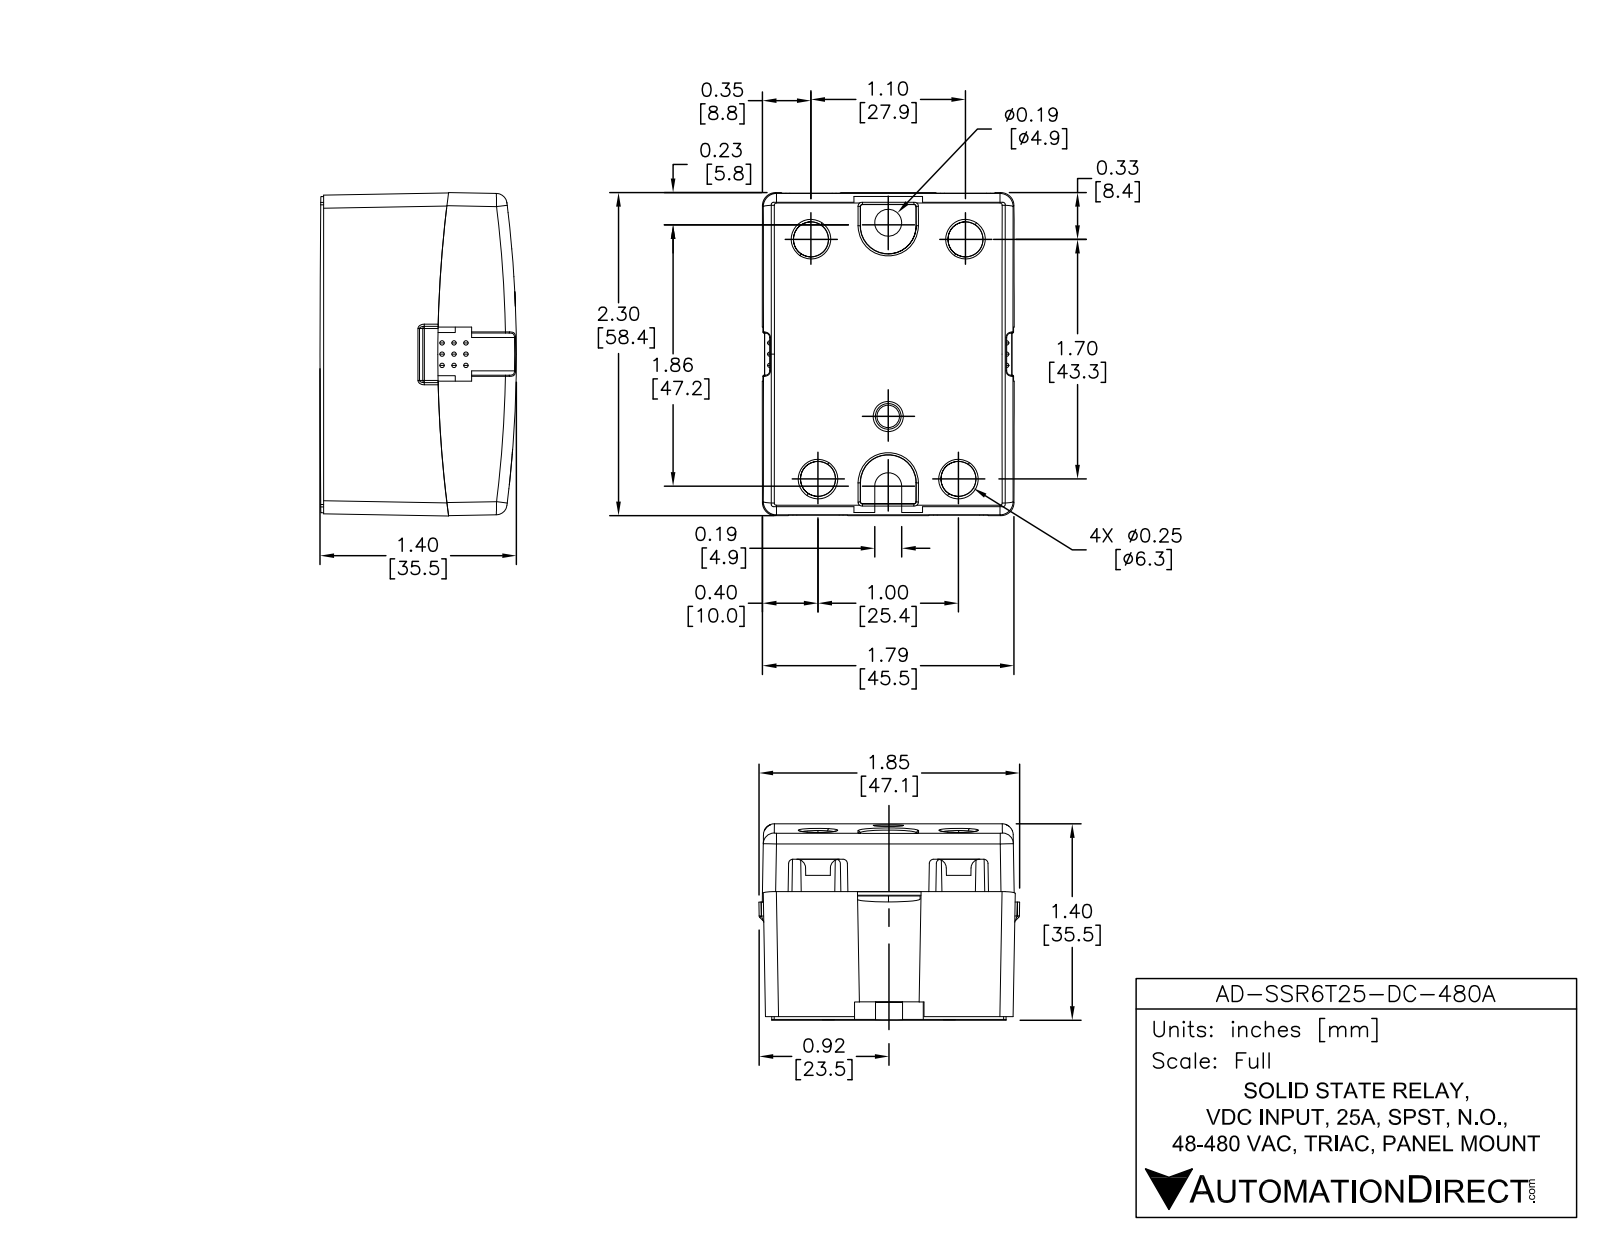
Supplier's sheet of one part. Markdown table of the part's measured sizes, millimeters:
| quantity | value |
| --- | --- |
| part name | AD-SSR6T25-DC-480A |
| STEP written by | SolidWorks 2013 (AUTOMOTIVE_DESIGN) |
| units | millimeters |
| bodies | 3 solids, 251 faces (145 planar, 95 cylindrical, 11 other) |
| overall size | 58.4 × 45.5 × 35.6 |
| volume | 84 230 mm³ |
| surface area | 17 040 mm² |
| round holes (diameter × count) | 6.4 × 4, 4.8 × 1 |
| round bosses / shafts (diameter × count) | 10.2 × 2, 8.9 × 2, 7.6 × 2, 6.4 × 2, 5.1 × 2, 5.1 × 2 |
| partial cylindrical surfaces (radius × count) | 0.8 × 6, 0.3 × 4, 1 × 4, 12.7 × 4, 4.9 × 2, 2.4 × 1, 12.7 × 1, 12.7 × 1 |
| main face-to-face distances | 45.5, 58.4, 29.6, 6.4, 23.3, 17, 26.9, 12.7, 45.7, 2 |
| hole center spacings | 14.1, 14.4, 25.4, 27.9, 43.2, 43.2, 47.7, 47.7 |
